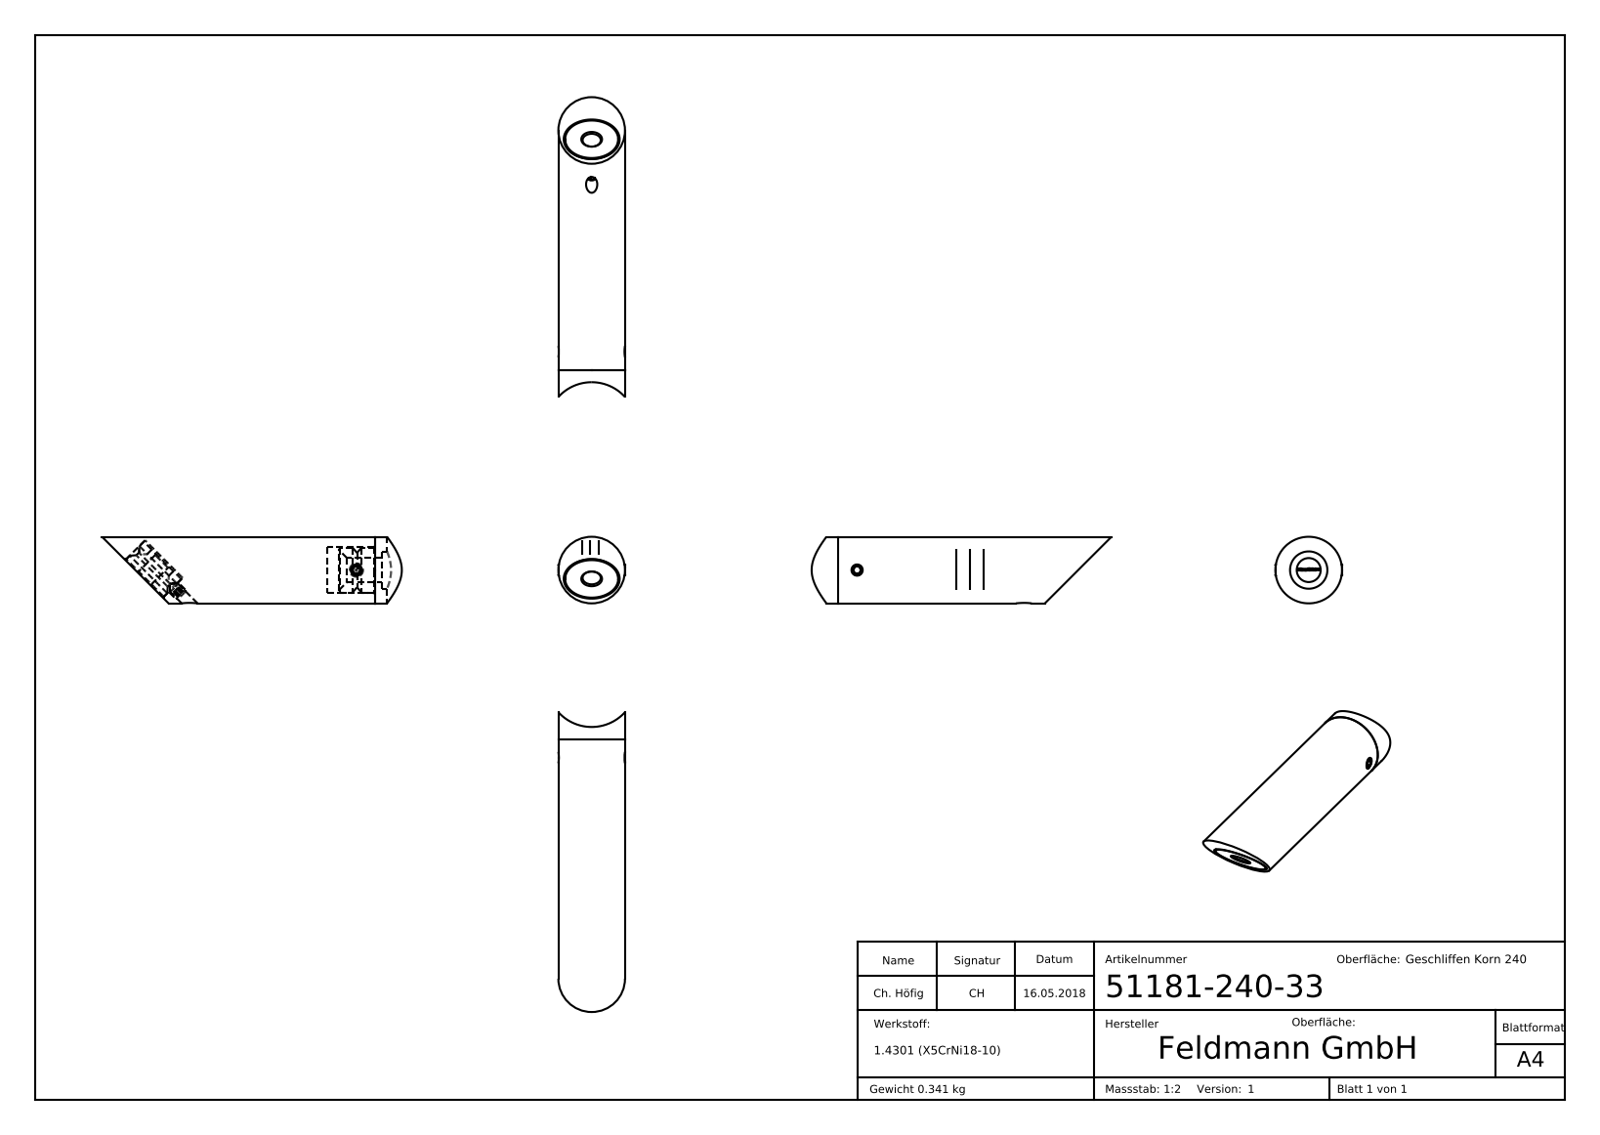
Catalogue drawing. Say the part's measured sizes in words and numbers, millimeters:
The part is named "51181-240-XX Teil3_51181-240-33 Teil3; 51181-240-XX Teil2_51181-240-XX Teil2; 51181-240-33; DIN914_DIN 914 M5x6 (+2 more)". Its 3-D file was written by "SolidWorks 2015 (CONFIG_CONTROL_DESIGN)". It is 6 solids with 361 faces: 176 planar, 37 cylindrical and 148 other. Overall it measures 112.55 by 25 by 25 millimeters. Its volume is 43 204 cubic millimeters and its surface area 14 457 square millimeters. Round holes: 2 of diameter 4.2, 1 of diameter 6.8, 1 of diameter 9, 1 of diameter 14, 1 of diameter 17, 1 of diameter 20. Round bosses or shafts: 2 of diameter 5, 1 of diameter 25, 1 of diameter 19.9, 1 of diameter 16.9, 1 of diameter 16.7. Partial cylindrical surfaces (rounded edges, fillets, slot ends): 1 of radius 16.85. The main face-to-face distances are 10.5, 9.8, 0.7, 18, 2.5, 20.5, 17.19, 16, 13.5, 4.5.
